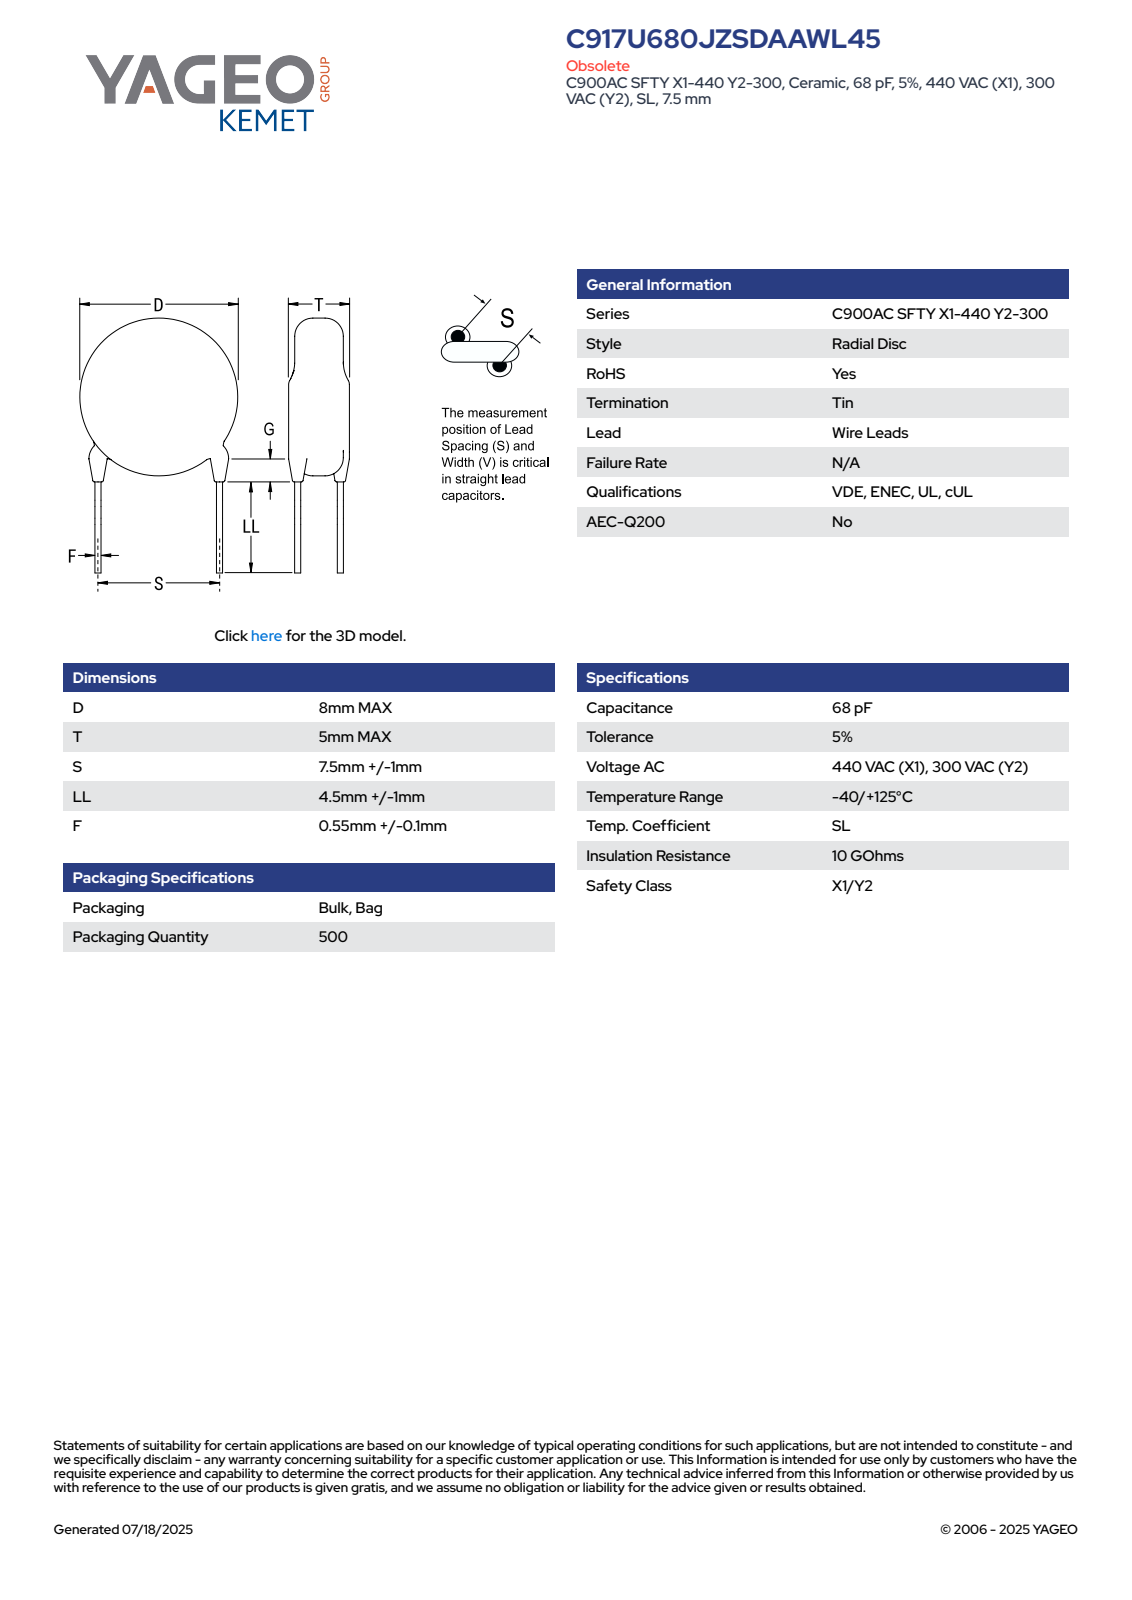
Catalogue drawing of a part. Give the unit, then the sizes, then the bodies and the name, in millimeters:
Units: millimetres
Overall size (bounding box): 13.82 × 8 × 5
Round bosses / shafts (diameter × count): ⌀0.65 ×2, ⌀8 ×1
Main face-to-face distances: 5, 10.28, 9.36, 0.92, 0.4, 1.04, 3.77, 0.57, 2.73, 2.84
Volume: 247 mm³ · Surface area: 240 mm²
Bodies: 4 solids, 83 faces (61 planar, 6 cylindrical, 16 other)
Part name (STEP PRODUCT): CCD_STC900_D8T5S7.5LL5.5F0.65G3
STEP written by: SolidWorks 2014 (AUTOMOTIVE_DESIGN)
